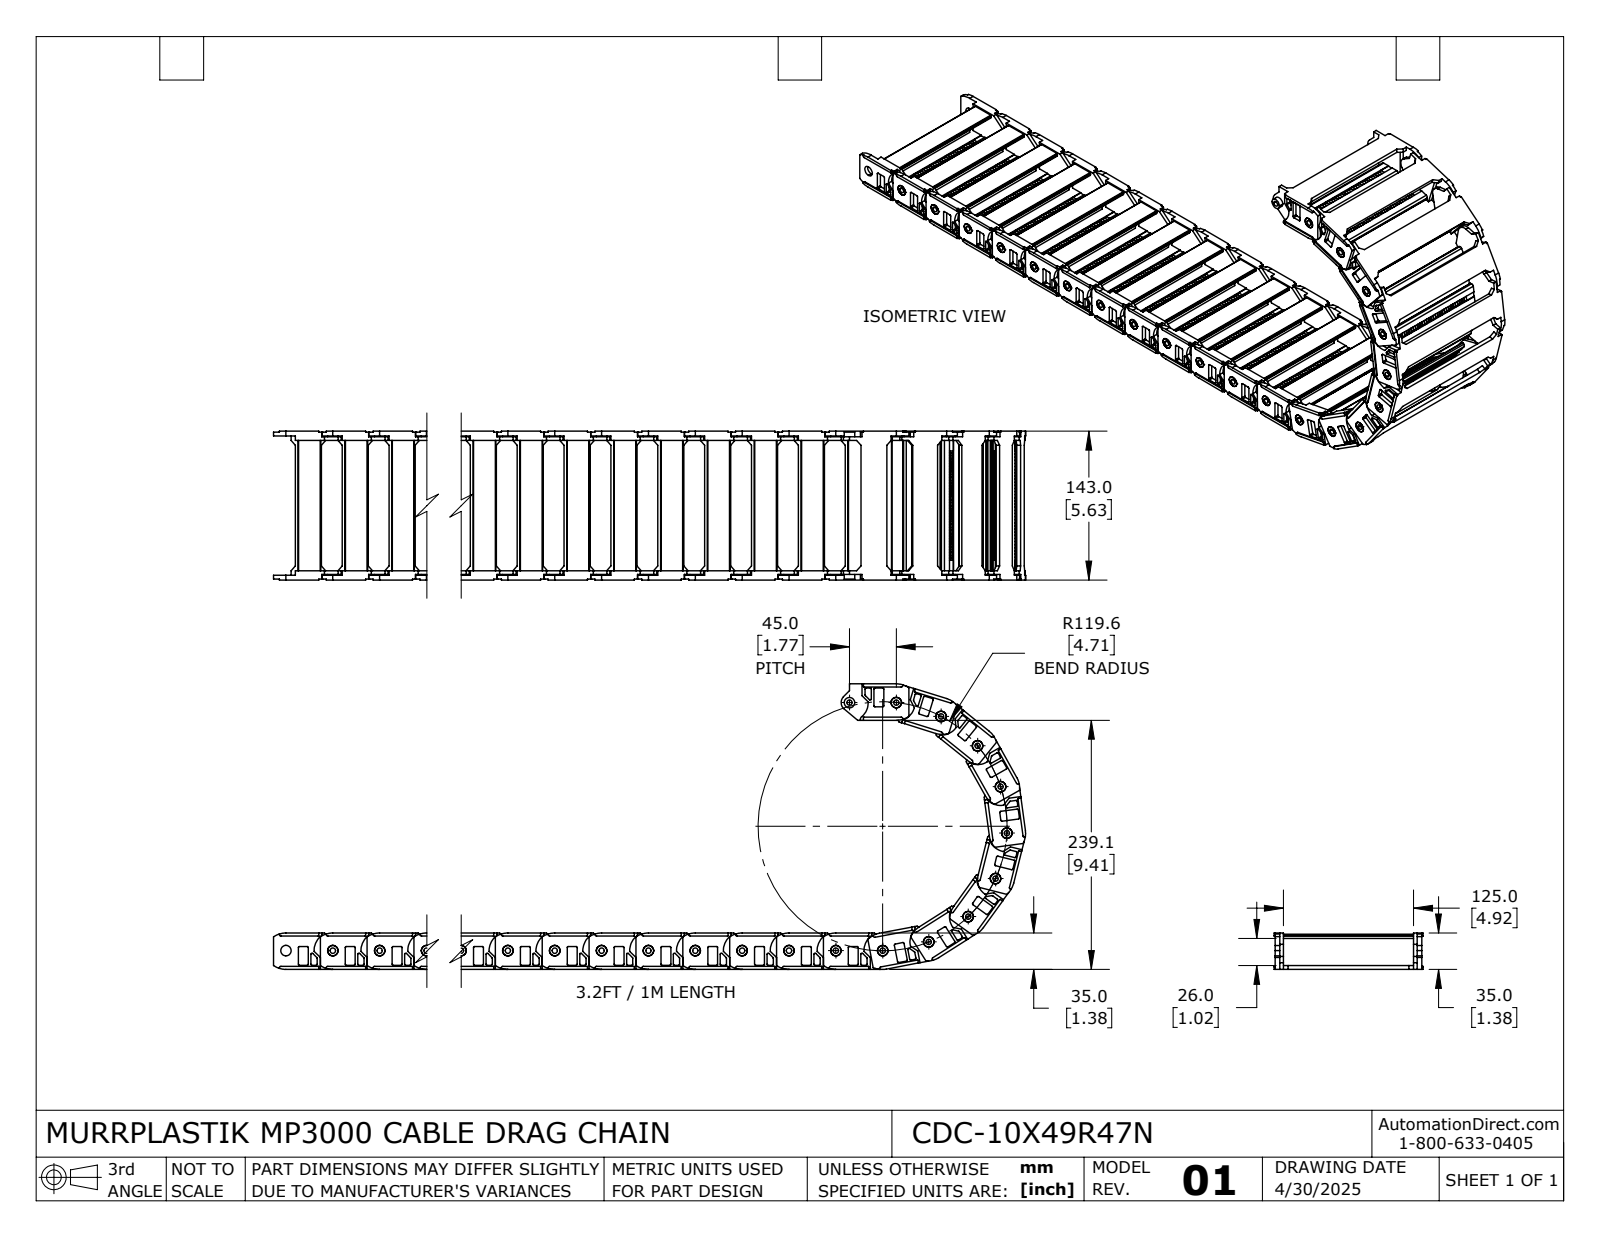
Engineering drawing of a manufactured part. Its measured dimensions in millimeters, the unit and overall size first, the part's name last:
Units: millimetres
Overall size (bounding box): 734.23 × 274.18 × 143
Round holes (diameter × count): ⌀5.1 ×22, ⌀10.1 ×22
Round bosses / shafts (diameter × count): ⌀10 ×22
Partial cylindrical surfaces — rounded edges, fillets, slot ends (radius × count): R1 ×176, R0.5 ×88, R1.5 ×44, R2 ×44, R21 ×44, R2.8 ×22, R8 ×22, R18 ×22
Main face-to-face distances: 4, 133, 30, 8, 33.8, 3.8, 29.8, 3.7, 137.3, 4.3
Hole centre spacings: 45, 90, 135, 180, 225, 44.98, 270, 315
Volume: 913 059 mm³ · Surface area: 573 607 mm²
Bodies: 22 solids, 6160 faces (5060 planar, 1100 cylindrical, 0 other)
Part name (STEP PRODUCT): CDC-10X49R47N
STEP written by: SolidWorks 2024 (AUTOMOTIVE_DESIGN)
